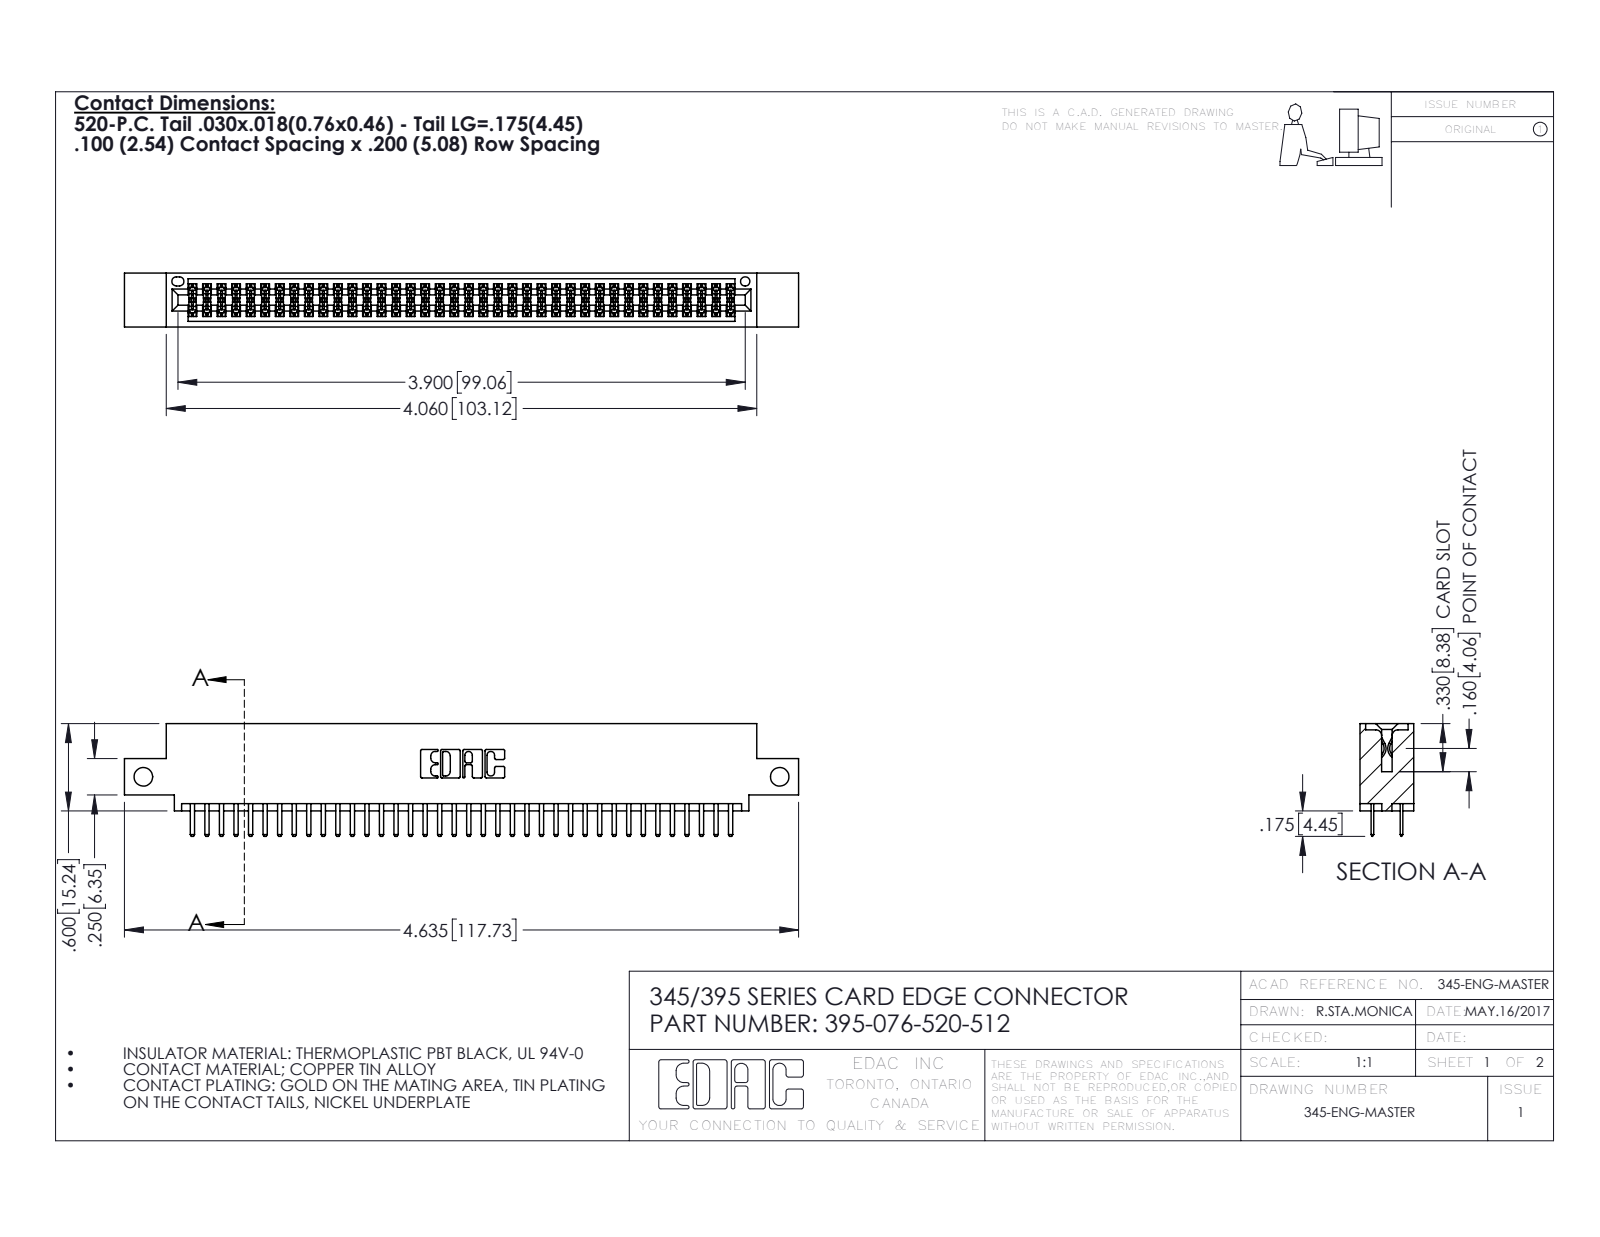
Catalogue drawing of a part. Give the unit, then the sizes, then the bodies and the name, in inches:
Units: inches
Overall size (bounding box): 4.635 × 0.775 × 0.37
Round holes (diameter × count): ⌀0.128 ×2, ⌀0.064 ×1
Partial cylindrical surfaces — rounded edges, fillets, slot ends (radius × count): R0.006 ×114, R0.01 ×80, R0.01 ×22, R0.007 ×6, R0.031 ×6, R0.026 ×3, R0.014 ×2, R0.019 ×2
Main face-to-face distances: 0.298, 0.072, 0.2, 0.37, 0.098, 0.272, 0.025, 0.225, 0.022, 0.072
Hole centre spacings: 4.375
Volume: 0.684 in³ · Surface area: 25.38 in²
Bodies: 77 solids, 4234 faces (2744 planar, 1490 cylindrical, 0 other)
Part name (STEP PRODUCT): 345-292-001_345-293-120; 395-076-520-512; 345 Part_0.110 Offset - Side Mount
STEP written by: SolidWorks 2016 (CONFIG_CONTROL_DESIGN)
